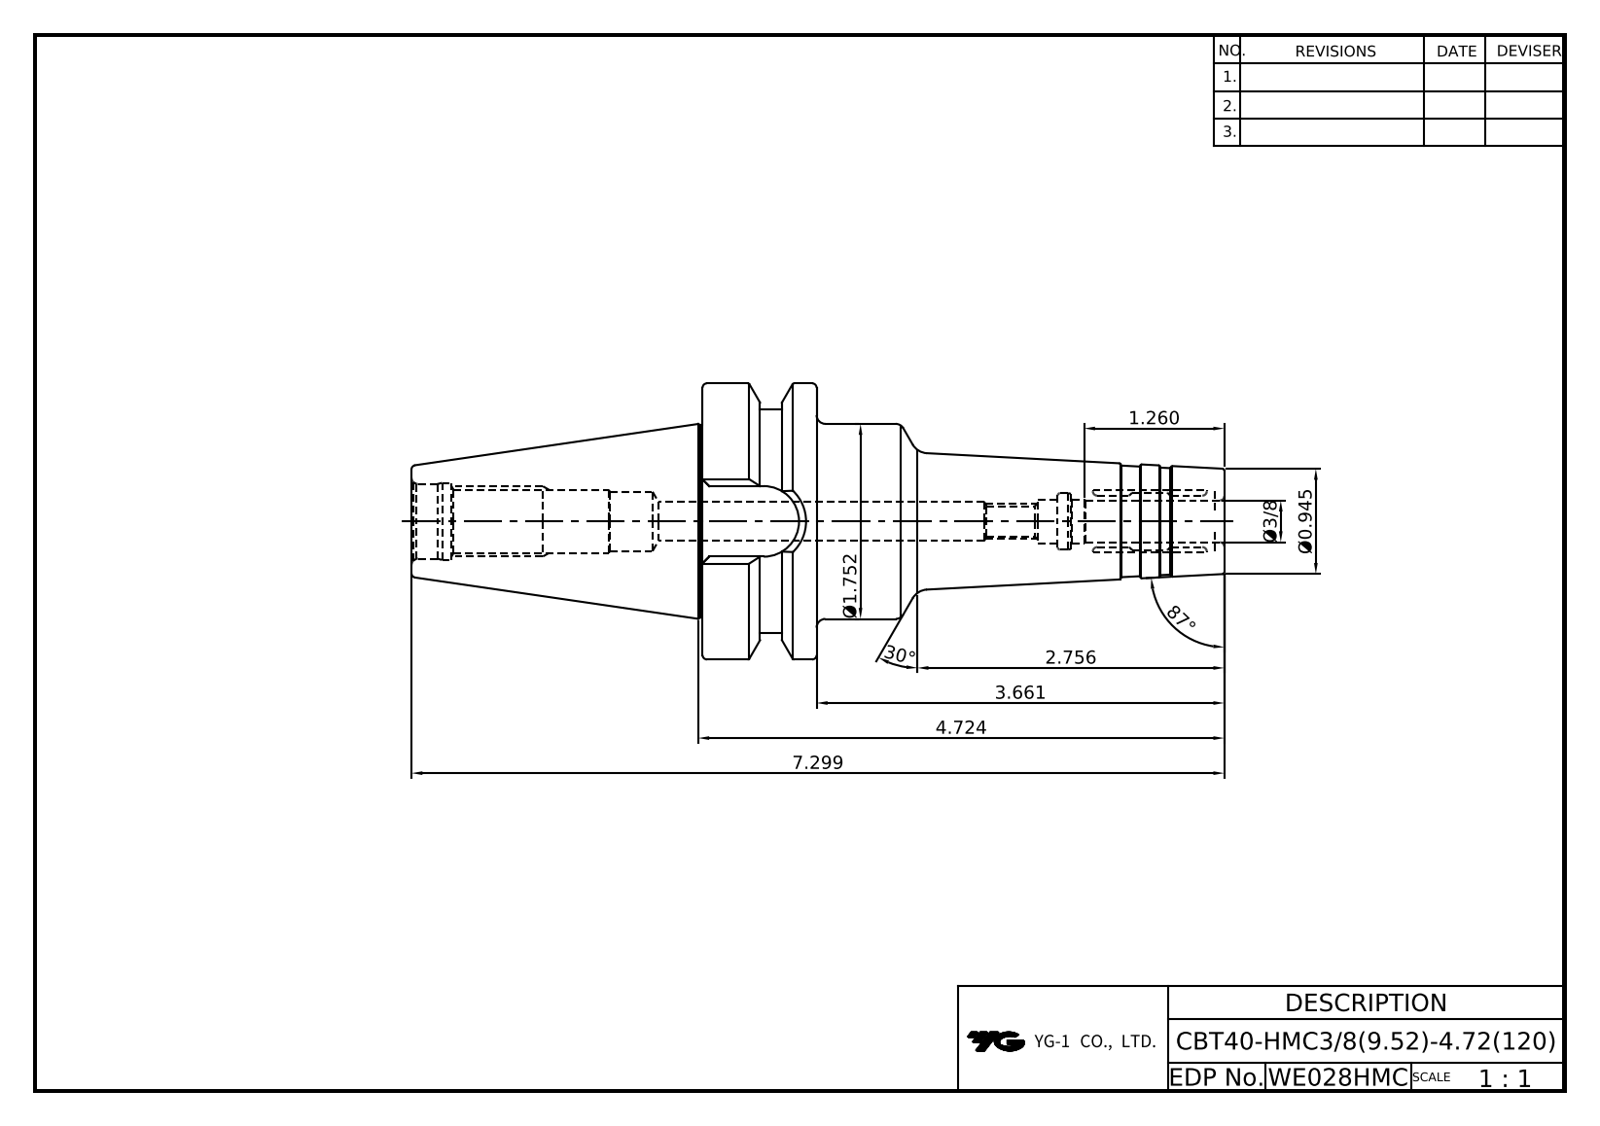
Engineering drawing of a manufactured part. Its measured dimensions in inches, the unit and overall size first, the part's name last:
Units: inches
Overall size (bounding box): 7.299 × 2.48 × 2.48
Round holes (diameter × count): ⌀0.272 ×1, ⌀0.354 ×1, ⌀0.368 ×1, ⌀0.392 ×1, ⌀0.531 ×1, ⌀0.545 ×1, ⌀0.669 ×1, ⌀0.693 ×1
Round bosses / shafts (diameter × count): ⌀2.48 ×1, ⌀2.008 ×1, ⌀1.752 ×1, ⌀1.732 ×1
Partial cylindrical surfaces — rounded edges, fillets, slot ends (radius × count): R0.317 ×1
Main face-to-face distances: 1.024, 4.685, 3.661, 1.78, 0.713, 0.311, 3.972, 0.516, 0.197, 0.508
Volume: 11.73 in³ · Surface area: 52.14 in²
Bodies: 1 solid, 83 faces (24 planar, 17 cylindrical, 42 other)
Part name (STEP PRODUCT): LO-CBT40-HMC9.35-120
STEP written by: Autodesk Inventor 2022 (AUTOMOTIVE_DESIGN)
